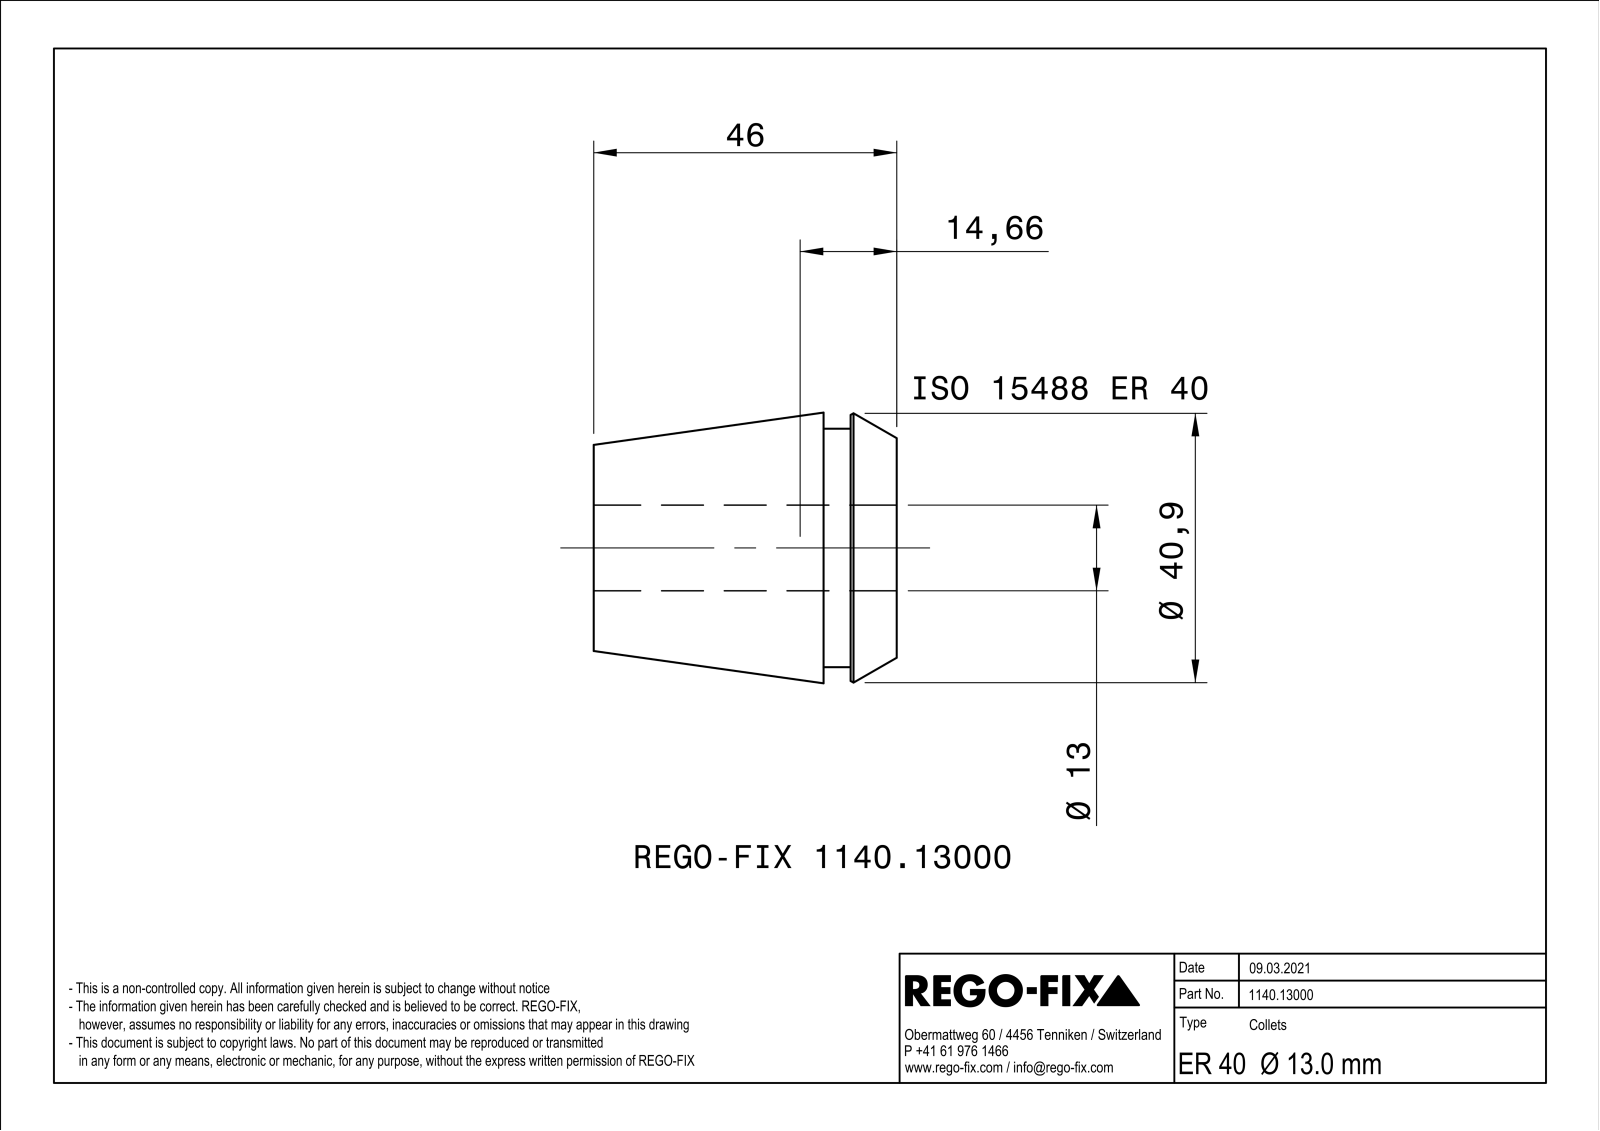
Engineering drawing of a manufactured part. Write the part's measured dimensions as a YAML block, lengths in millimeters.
part_name: "NOCUT"
step_written_by: "SIEMENS PLM Software Solid Edge ST10 (AUTOMOTIVE_DESIGN)"
units: millimeters
bodies: {solids: 1, faces: 177, planar: 88, cylindrical: 9, other: 80}
overall_size: [46, 40.99, 40.99]
volume: 34145
surface_area: 22986
round_holes:
  - {diameter: 13, count: 1}
round_bosses_or_shafts:
  - {diameter: 36.2, count: 1}
face_to_face_distances: [1, 46, 11.1, 34.9, 7, 4.1, 39, 7.5, 0.5, 3.6]
